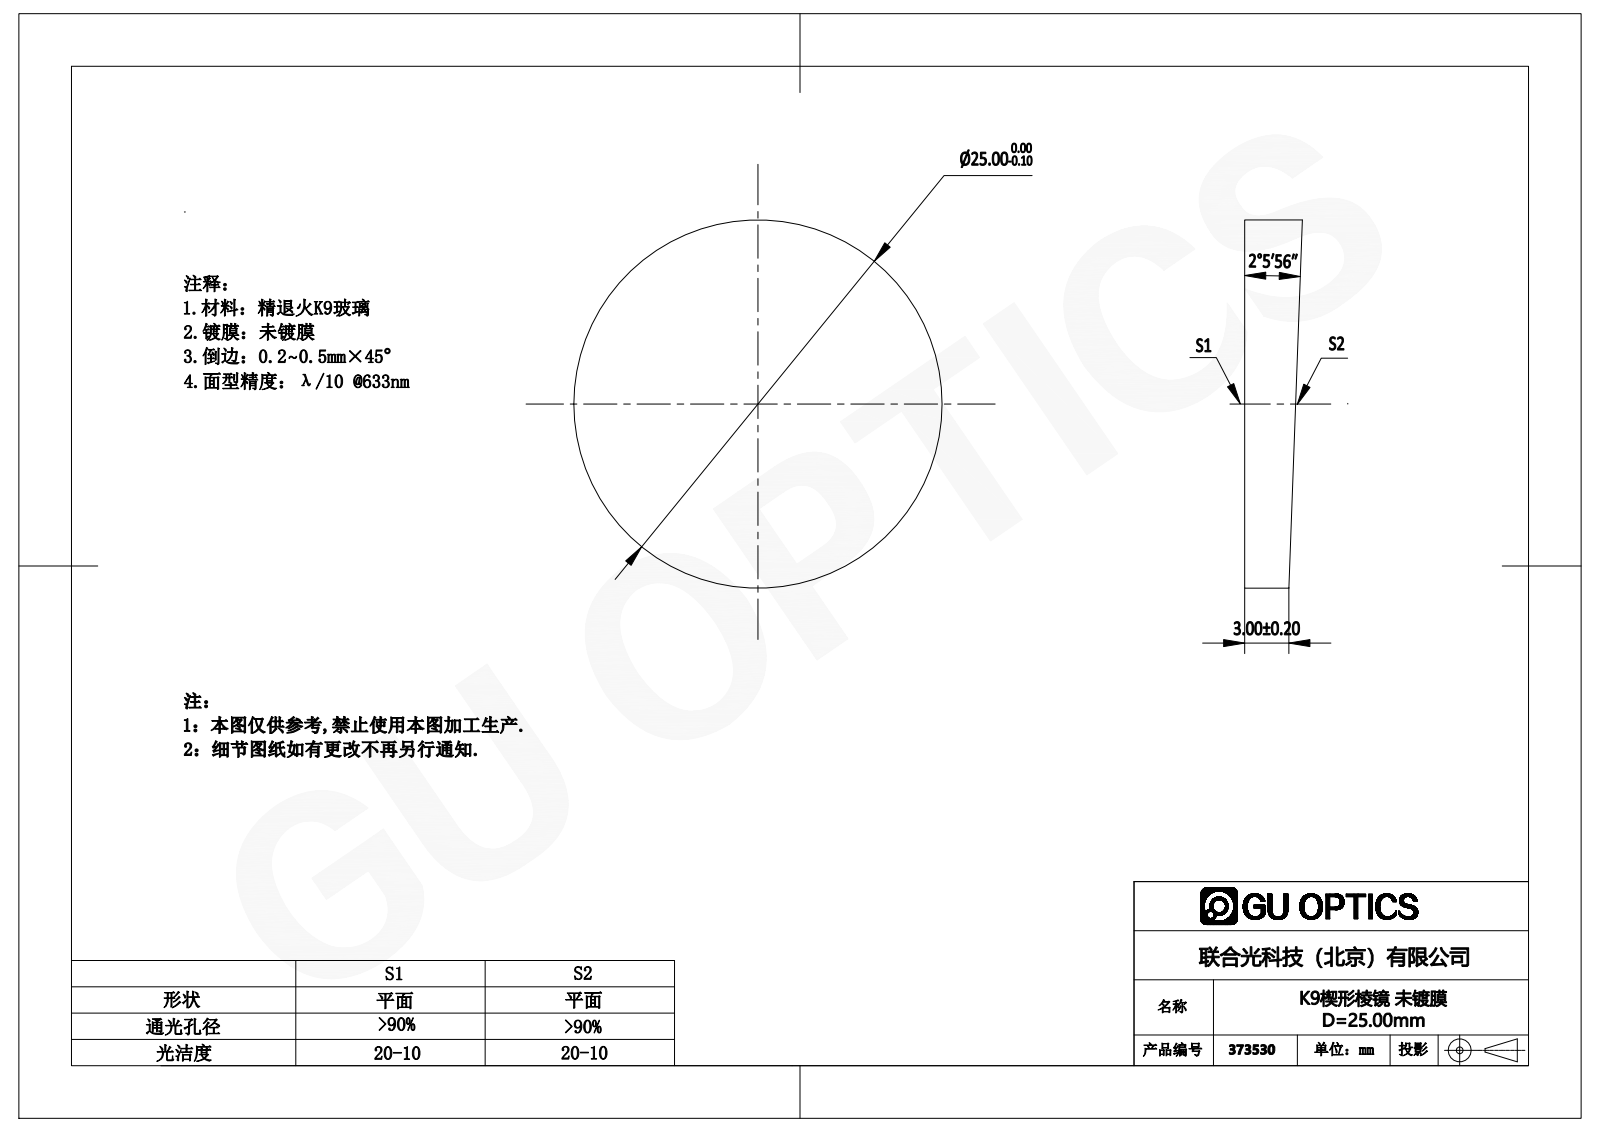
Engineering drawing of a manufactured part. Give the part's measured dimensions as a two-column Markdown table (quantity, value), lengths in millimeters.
| quantity | value |
| --- | --- |
| part name | 373530 |
| STEP written by | SolidWorks 2016 (CONFIG_CONTROL_DESIGN) |
| units | millimeters |
| bodies | 1 solid, 4 faces (2 planar, 2 cylindrical, 0 other) |
| overall size | 25 × 25 × 3.92 |
| volume | 1 697 mm³ |
| surface area | 1 254 mm² |
| round bosses / shafts (diameter × count) | 25 × 1 |
